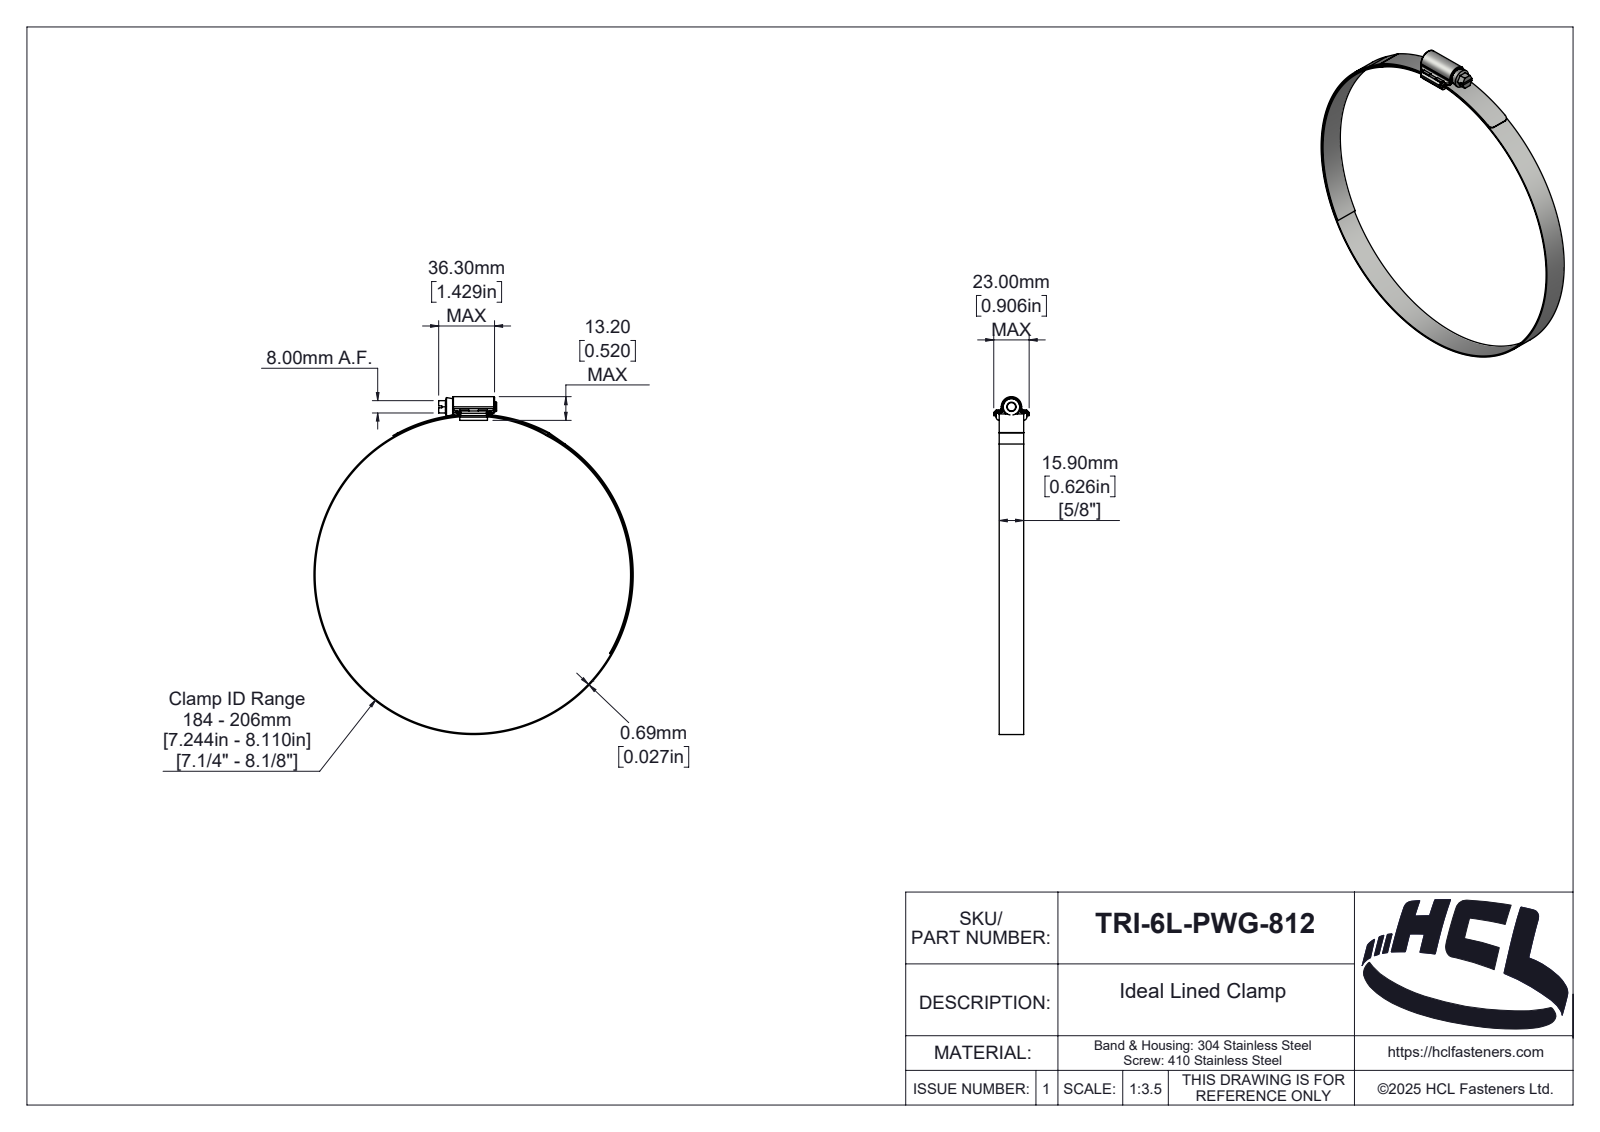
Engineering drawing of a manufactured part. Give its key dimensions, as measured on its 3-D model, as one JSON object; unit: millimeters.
{"part_name": "TRI-6L-PWG-812", "step_written_by": "SolidWorks 2025 (AUTOMOTIVE_DESIGN)", "units": "millimeters", "bodies": {"solids": 4, "faces": 268, "planar": 87, "cylindrical": 102, "other": 79}, "overall_size": [219.39, 207.38, 23], "volume_mm3": 15274, "surface_area_mm2": 35093, "round_holes": [[206, 1]], "round_bosses_or_shafts": [[207.38, 1], [10.7, 1], [6, 1]], "partial_cylinders_radius": [[1, 14], [0.5, 4], [1.5, 4], [2, 3], [0.1, 2], [2.1, 2], [3, 2], [0.46, 1]], "face_to_face_distances": [15.9, 2, 0.69, 17.9, 4.9, 1.2, 4.55, 3.35, 15.35, 2.55]}
